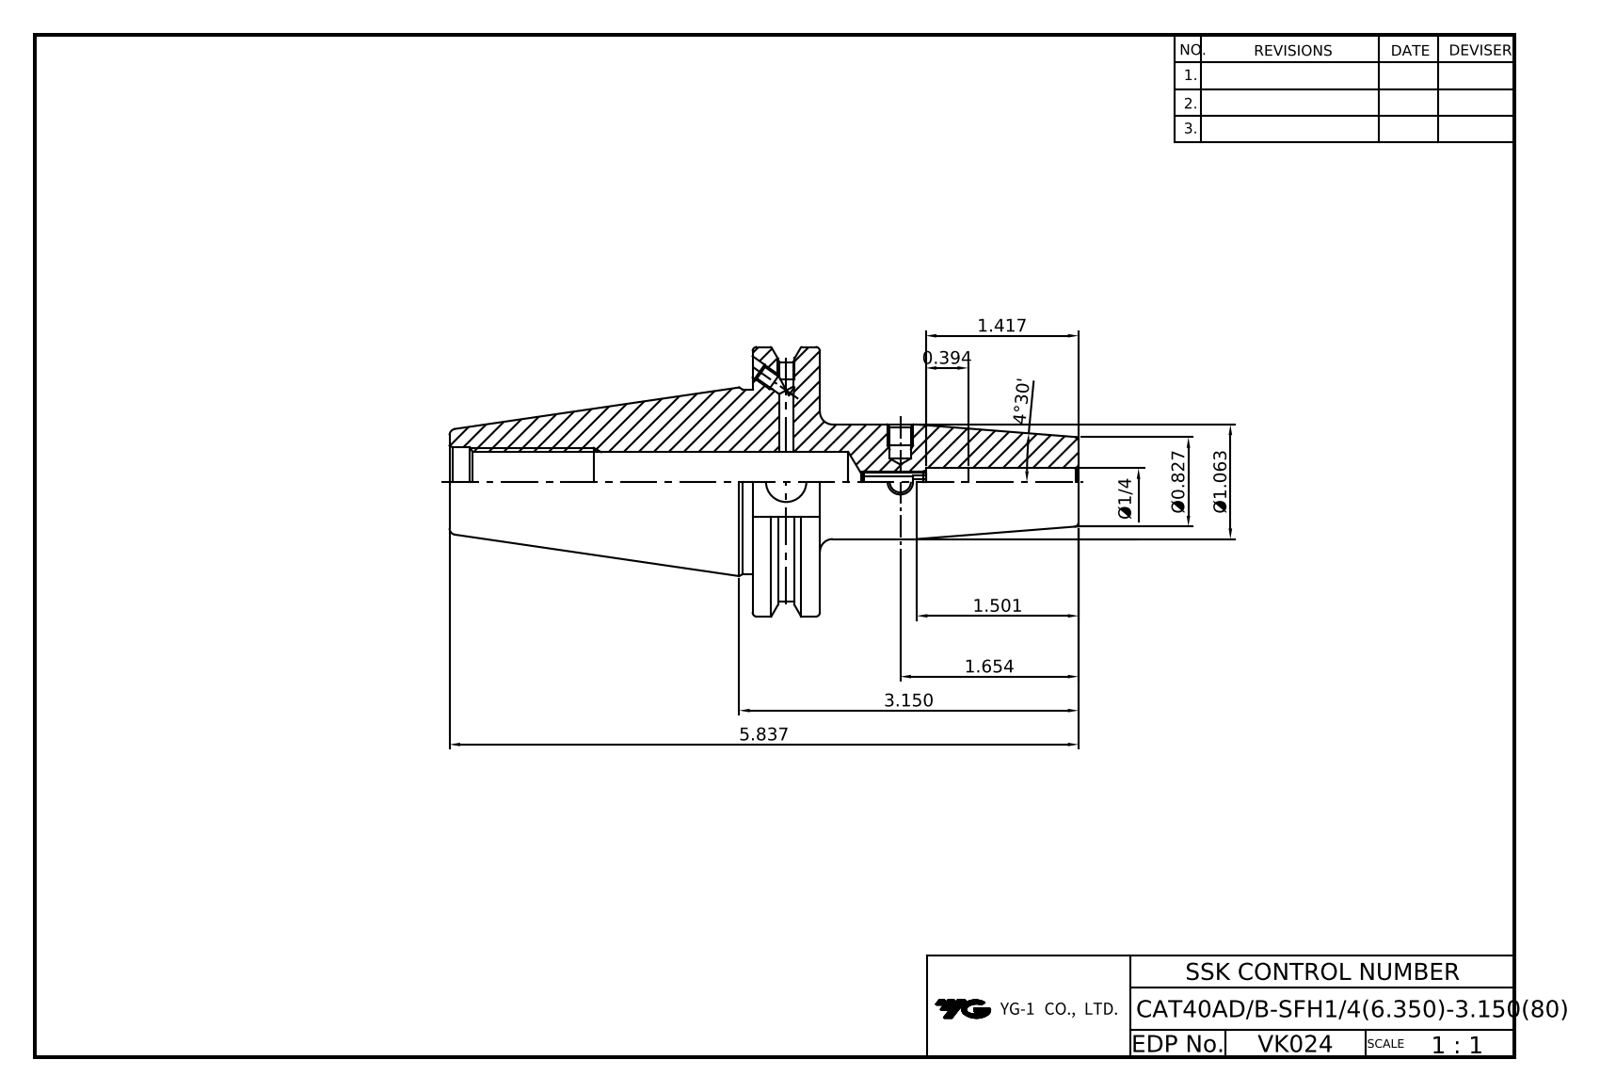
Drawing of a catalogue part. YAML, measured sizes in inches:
part_name: "LO-CAT40ADB-SFH6.35-80"
step_written_by: "Autodesk Inventor 2024 (AUTOMOTIVE_DESIGN)"
units: inches
bodies: {solids: 1, faces: 88, planar: 37, cylindrical: 29, other: 22}
overall_size: [5.837, 2.5, 2.405]
volume: 7.86
surface_area: 41.25
round_holes:
  - {diameter: 0.128, count: 4}
  - {diameter: 0.157, count: 2}
  - {diameter: 0.165, count: 2}
  - {diameter: 0.163, count: 1}
  - {diameter: 0.25, count: 1}
  - {diameter: 0.297, count: 1}
  - {diameter: 0.375, count: 1}
  - {diameter: 0.512, count: 1}
  - {diameter: 0.527, count: 1}
  - {diameter: 0.642, count: 1}
round_bosses_or_shafts:
  - {diameter: 2.5, count: 1}
  - {diameter: 1.717, count: 1}
  - {diameter: 1.063, count: 1}
partial_cylinders:
  - {radius: 1.108, count: 1}
face_to_face_distances: [0.625, 3.025, 2.4, 1.874, 0.645, 2.812, 3.437, 5.837, 3.05, 0.238]
